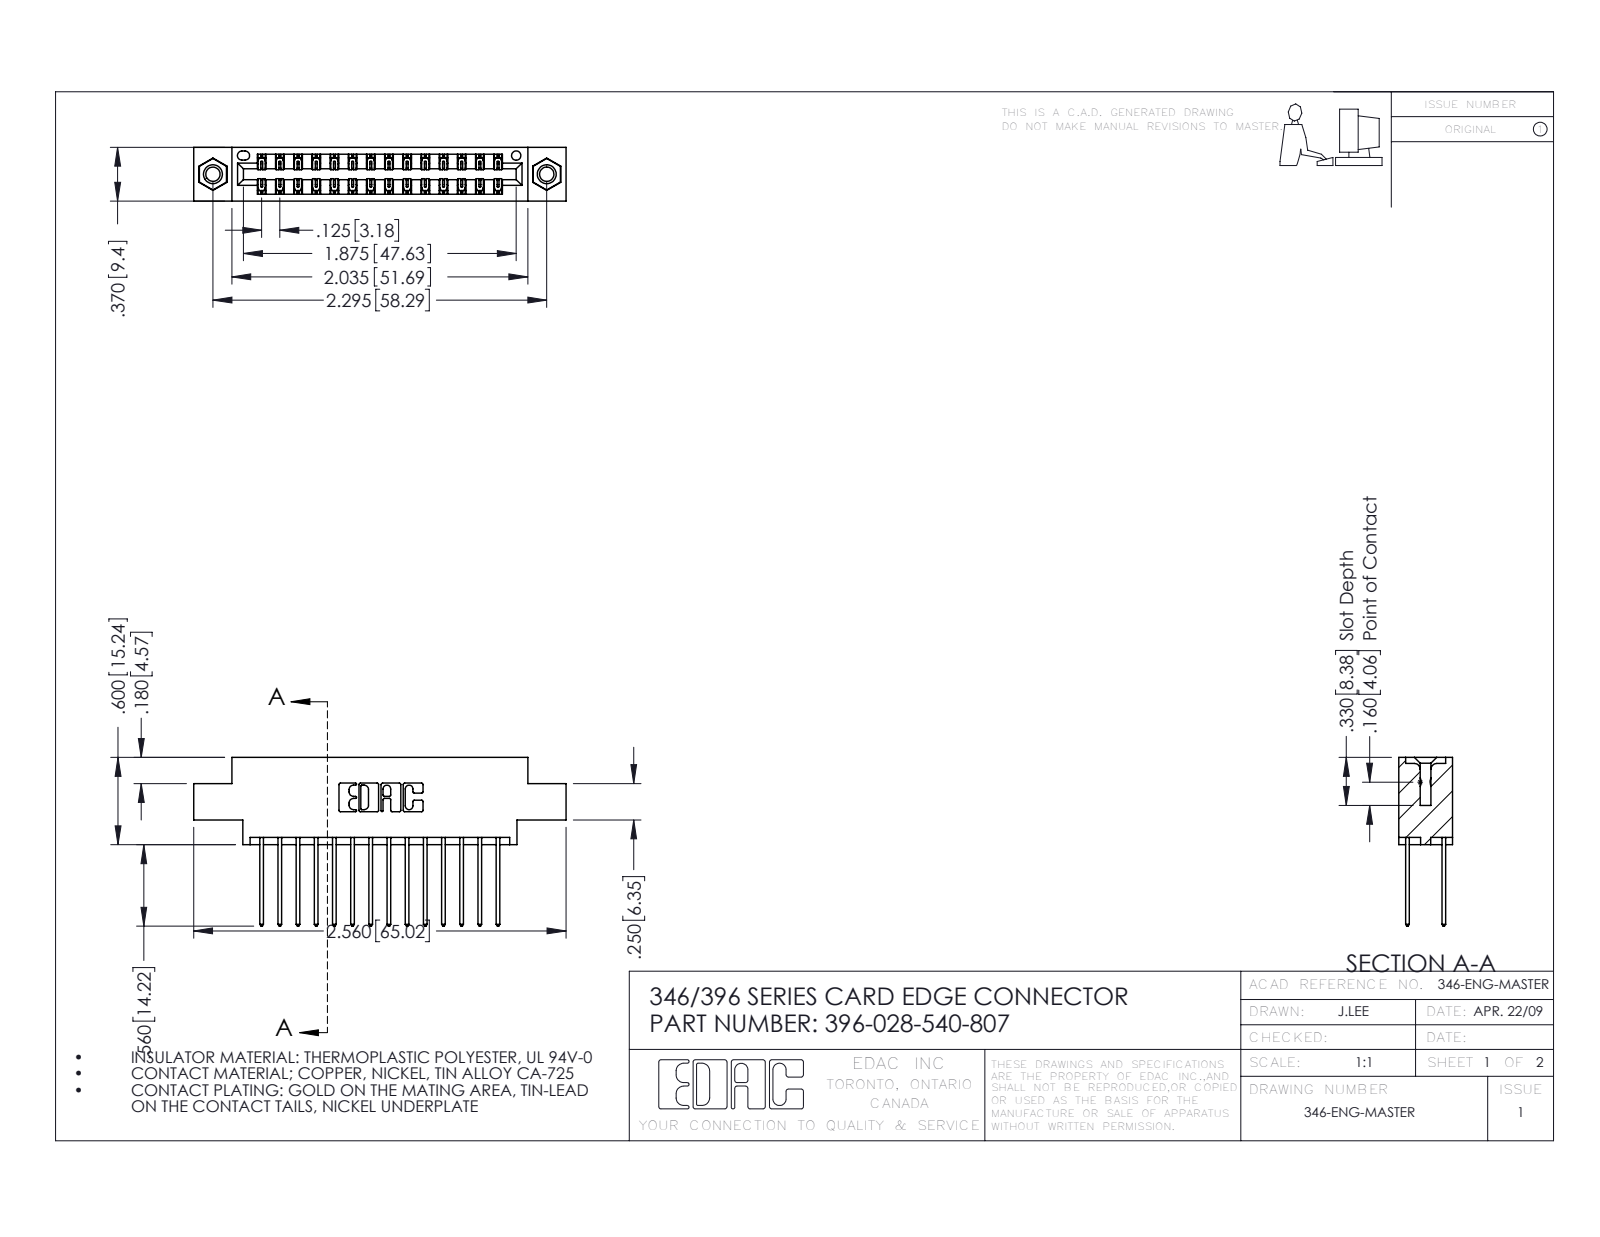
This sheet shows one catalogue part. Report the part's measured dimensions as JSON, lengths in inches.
{"part_name": "396-028-540-807; 346 Part_0.170 Offset - 0.156 Dia-TI; 345-292-001_345-293-140; 345-250-001_345-250-005-103", "step_written_by": "SolidWorks 2016 (CONFIG_CONTROL_DESIGN)", "units": "inches", "bodies": {"solids": 31, "faces": 1642, "planar": 1092, "cylindrical": 534, "other": 16}, "overall_size": [2.56, 1.16, 0.37], "volume_in3": 0.37, "surface_area_in2": 13.34, "round_holes": [[0.098, 2], [0.125, 2], [0.156, 2], [0.064, 1]], "round_bosses_or_shafts": [[0.155, 2]], "partial_cylinders_radius": [[0.006, 42], [0.01, 28], [0.01, 22], [0.007, 6], [0.031, 6], [0.026, 3], [0.014, 2], [0.022, 2]], "face_to_face_distances": [0.048, 0.322, 0.25, 0.37, 0.072, 0.298, 0.025, 0.275, 0.222, 0.148], "hole_center_spacings": [0.246, 2.089, 2.295]}
